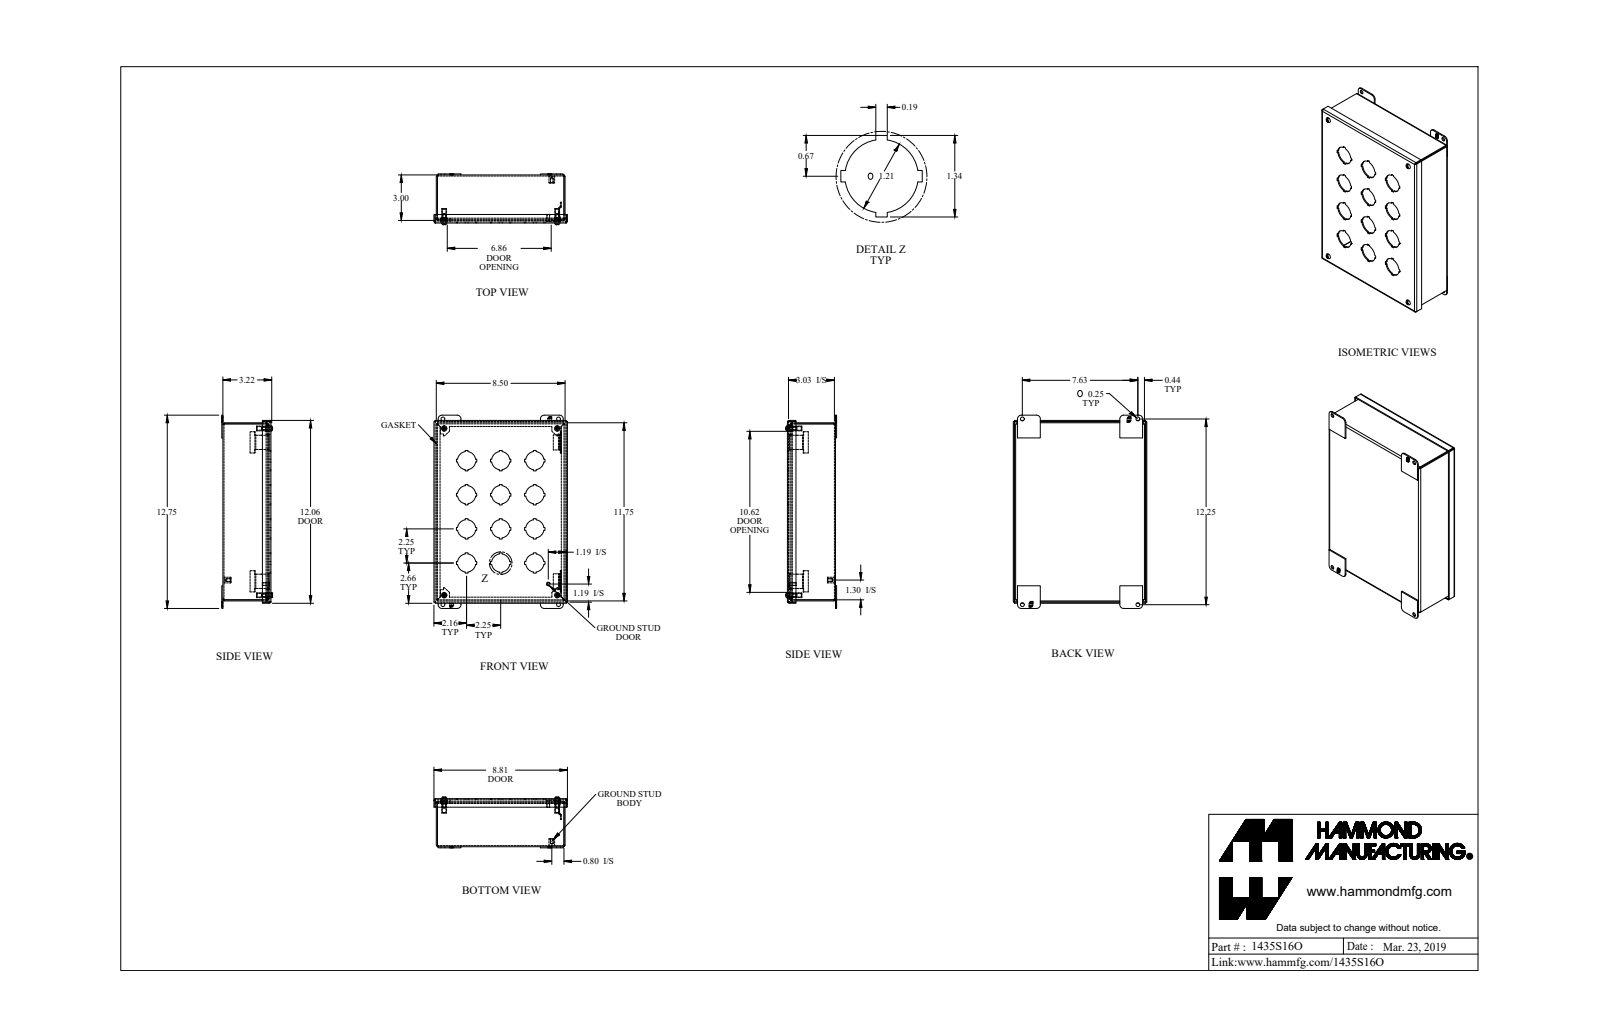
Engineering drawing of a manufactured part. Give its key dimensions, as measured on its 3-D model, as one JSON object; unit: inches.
{"part_name": "1435S16O_Default", "step_written_by": "SolidWorks 2019 (CONFIG_CONTROL_DESIGN)", "units": "inches", "bodies": {"solids": 23, "faces": 797, "planar": 567, "cylindrical": 200, "other": 30}, "overall_size": [12.75, 8.81, 3.354], "volume_in3": 28.91, "surface_area_in2": 768.3, "round_holes": [[1.21, 12], [0.25, 8], [0.065, 4], [0.239, 4], [0.253, 4], [0.406, 4], [0.156, 1]], "round_bosses_or_shafts": [[0.19, 5], [0.406, 4], [0.315, 4], [0.148, 4], [0.375, 1], [0.25, 1]], "partial_cylinders_radius": [[0.036, 12], [0.108, 12], [0.25, 8], [0.029, 4], [0.086, 4], [0.171, 4]], "face_to_face_distances": [0.072, 3.1, 3.172, 3.028, 8.428, 0.072, 11.678, 8.5, 8.356, 0.155], "hole_center_spacings": [2.25, 5.031, 3.182, 4.5, 7.46, 7.461, 7.569, 10.999]}
